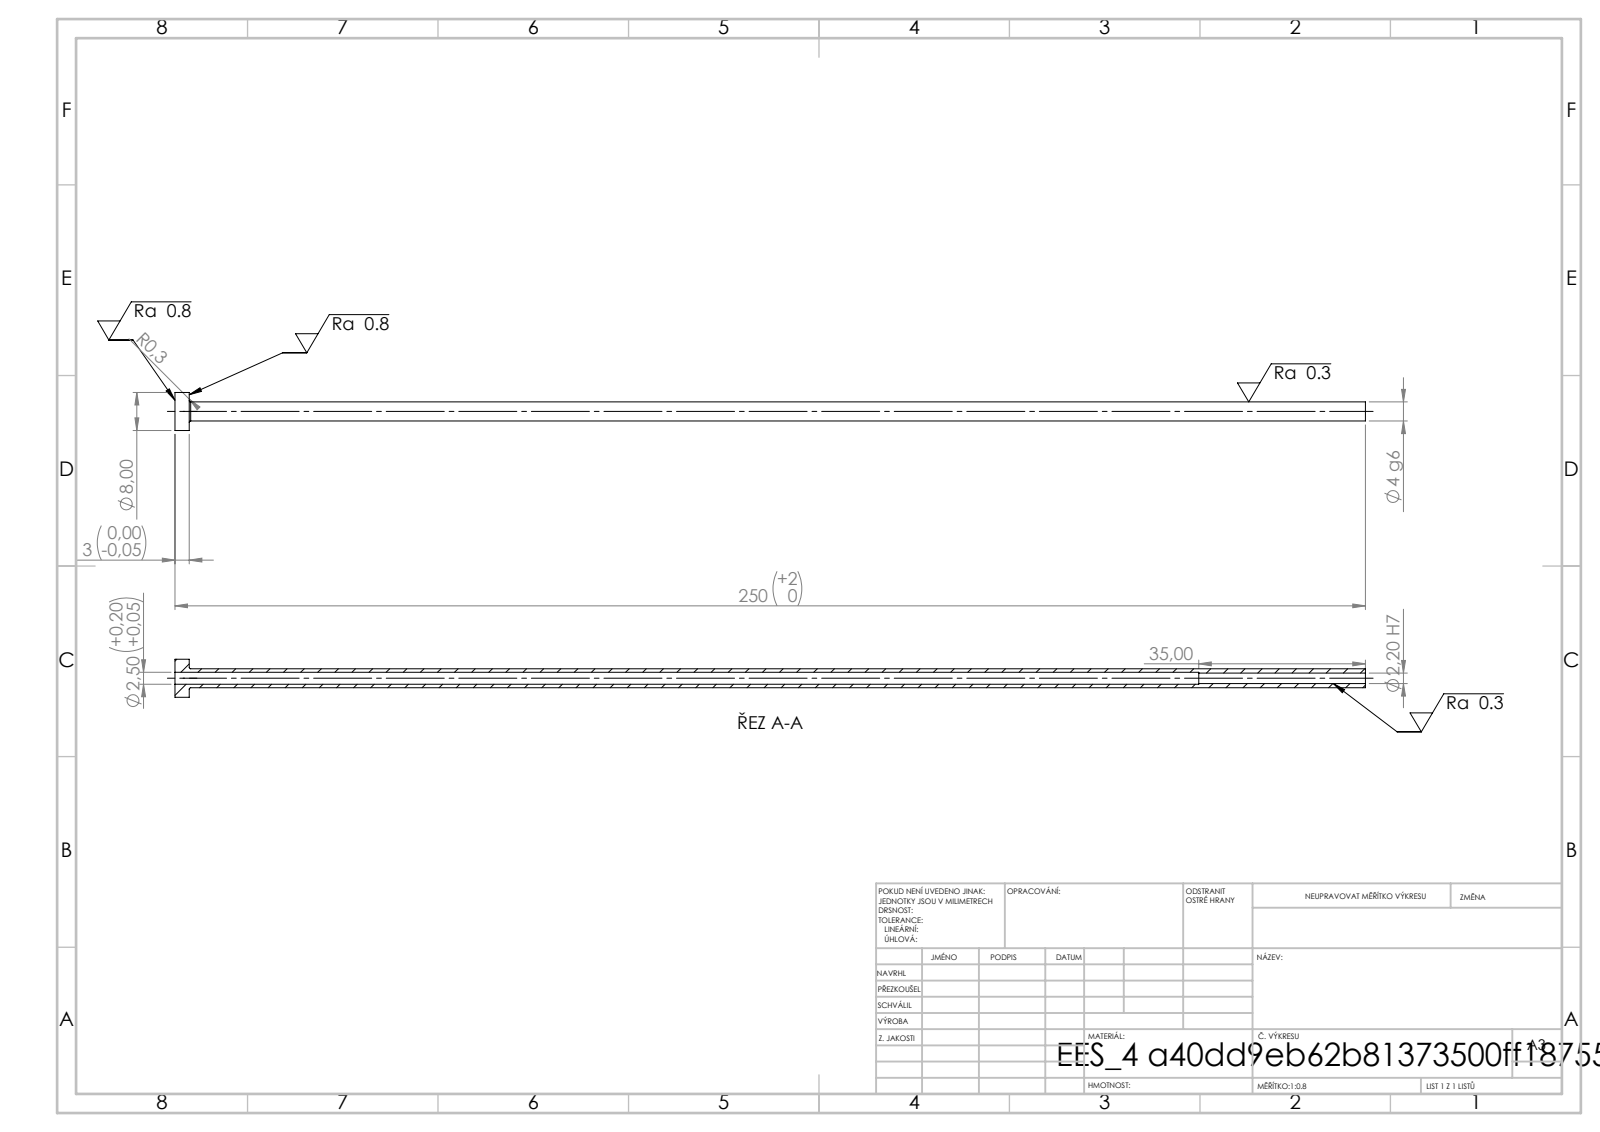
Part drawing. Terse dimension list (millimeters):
written by: SolidWorks 2019 (CONFIG_CONTROL_DESIGN)
unit: mm
bodies: 1 solid, 14 faces (4 planar, 8 cylindrical, 2 other)
size: 250 × 8 × 8
volume: 2 067 mm³; area: 5 201 mm²
holes: 1× ⌀2.2, 1× ⌀2.5
bosses: 1× ⌀8, 1× ⌀4
face distances: 3, 250, 247, 215, 212, 35
